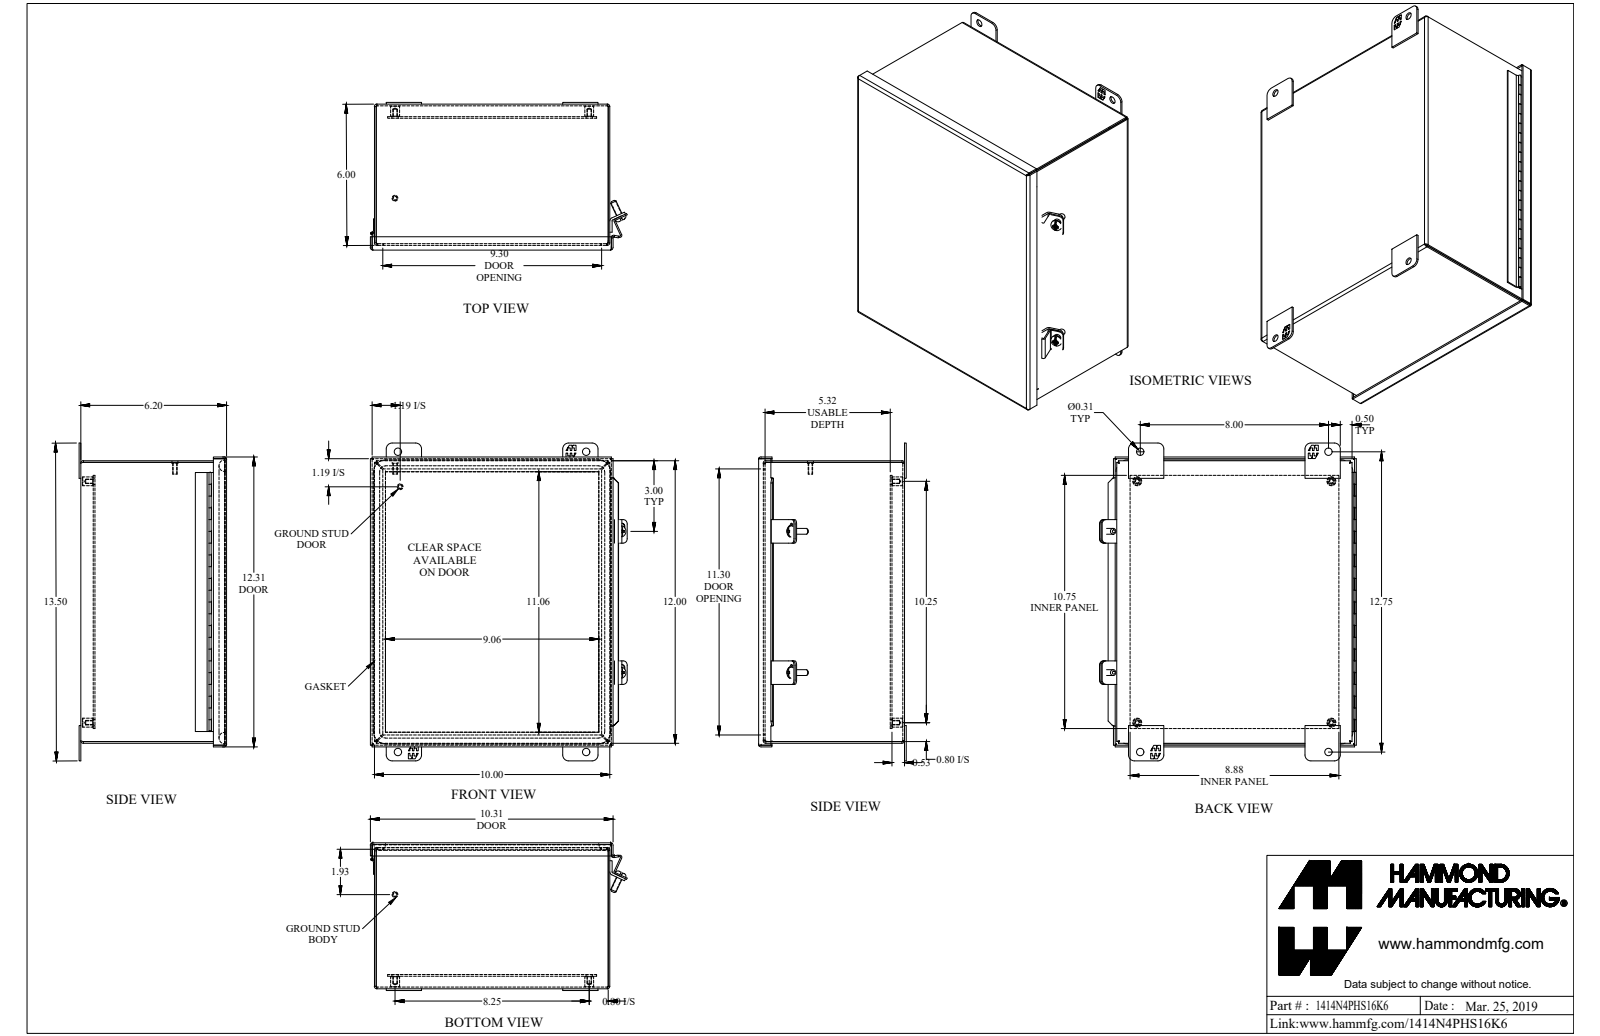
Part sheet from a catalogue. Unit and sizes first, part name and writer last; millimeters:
Units: millimetres
Overall size (bounding box): 342.9 × 277.15 × 162.29
Round holes (diameter × count): ⌀3.97 ×5, ⌀6.73 ×4, ⌀7.94 ×4, ⌀5.41 ×2, ⌀1.27 ×1
Round bosses / shafts (diameter × count): ⌀9.53 ×4, ⌀6.35 ×4, ⌀12.19 ×2, ⌀4.83 ×2, ⌀9.78 ×1, ⌀4.7 ×1, ⌀2.54 ×1, ⌀1.14 ×1
Partial cylindrical surfaces — rounded edges, fillets, slot ends (radius × count): R6.35 ×24, R0.91 ×13, R2.74 ×13, R4.78 ×8, R0.25 ×4, R3.57 ×4, R9.53 ×4, R12.68 ×4
Main face-to-face distances: 1.83, 155.57, 142.06, 13.51, 252.17, 157.4, 153.74, 302.97, 15.34, 11.68
Hole centre spacings: 208.81, 292.13, 334.21, 31.91, 209.55, 209.56, 260.35, 260.36
Volume: 848 360 mm³ · Surface area: 946 045 mm²
Bodies: 27 solids, 869 faces (576 planar, 200 cylindrical, 93 other)
Part name (STEP PRODUCT): 1414N4PHS16K6; COM42868; COM54180; STD26154 (+8 more)
STEP written by: ST-DEVELOPER v16.7 (AUTOMOTIVE_DESIGN)
